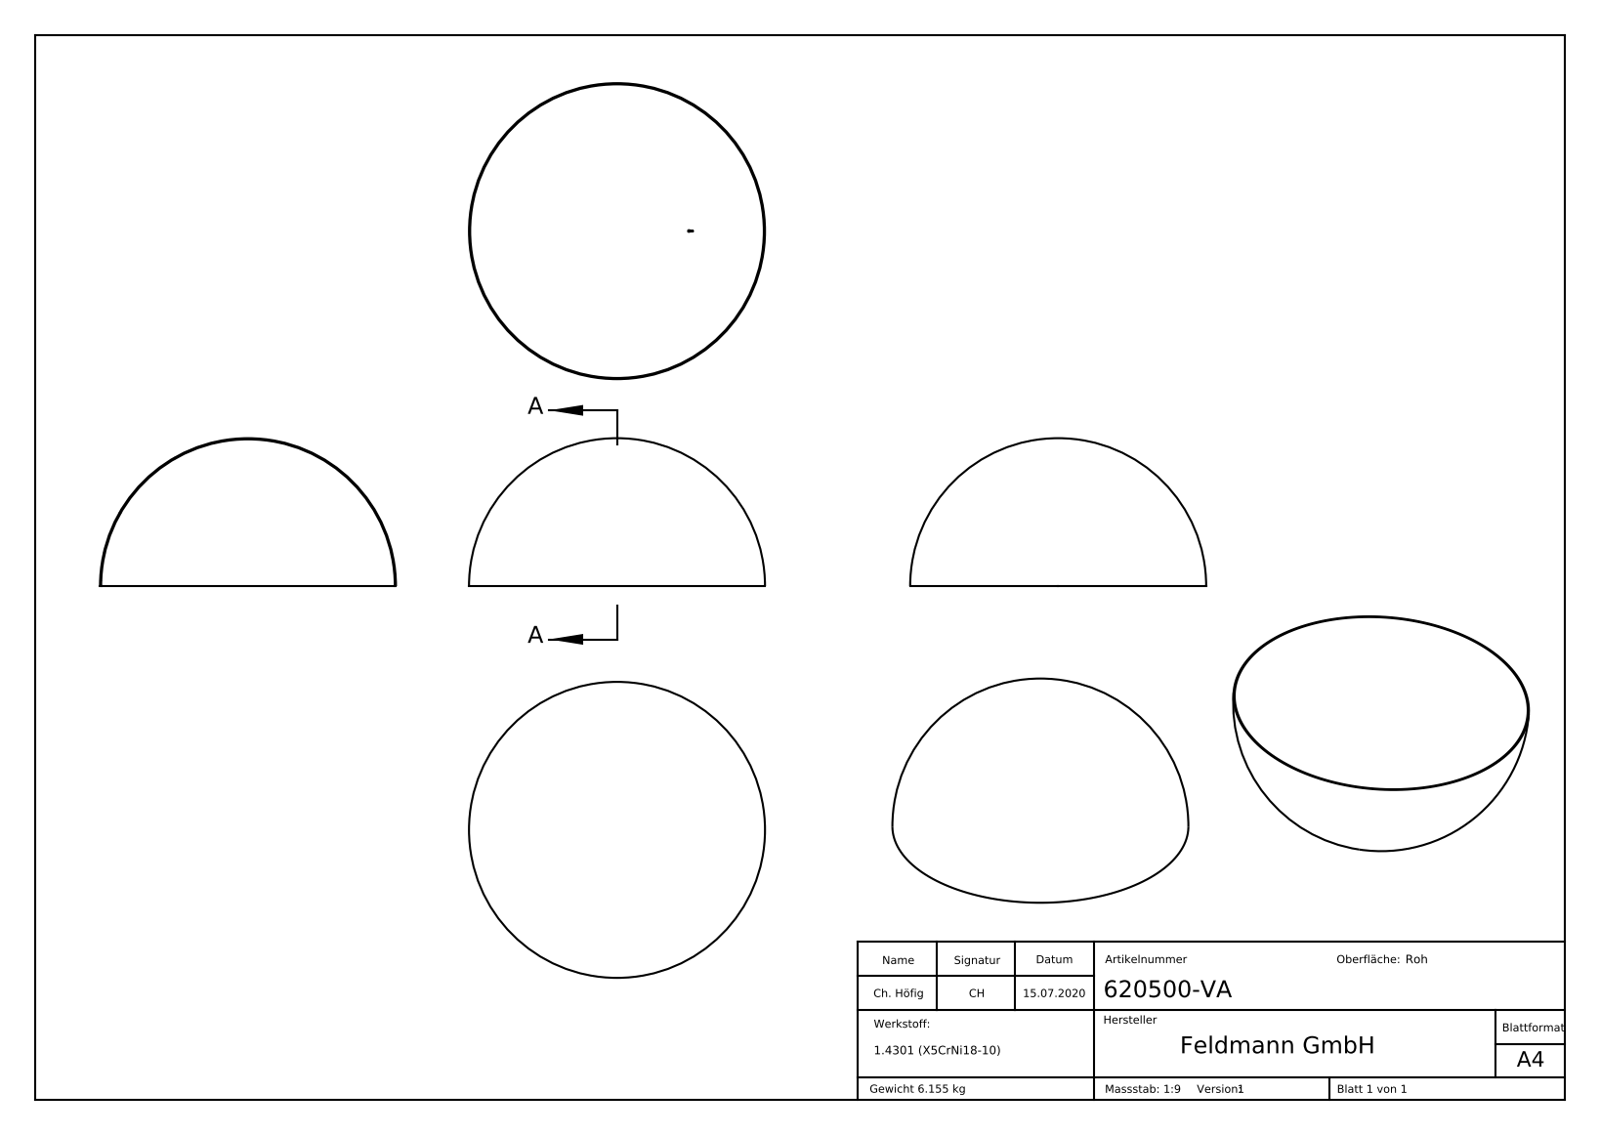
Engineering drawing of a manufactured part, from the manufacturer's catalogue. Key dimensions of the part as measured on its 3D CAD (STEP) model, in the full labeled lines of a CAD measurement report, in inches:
Part name (STEP PRODUCT): 620500-VA
STEP written by: SolidWorks 2018 (CONFIG_CONTROL_DESIGN)
Units: inches
Bodies: 1 solid, 217 faces (92 planar, 0 cylindrical, 125 other)
Overall size (bounding box): 19.685 × 19.685 × 9.843
Volume: 47.55 in³ · Surface area: 1 213 in²
Main face-to-face distances: 0.018, 0.021, 0.02, 0.024, 0.047, 0.022, 0.032, 0.052, 0.033, 0.012
